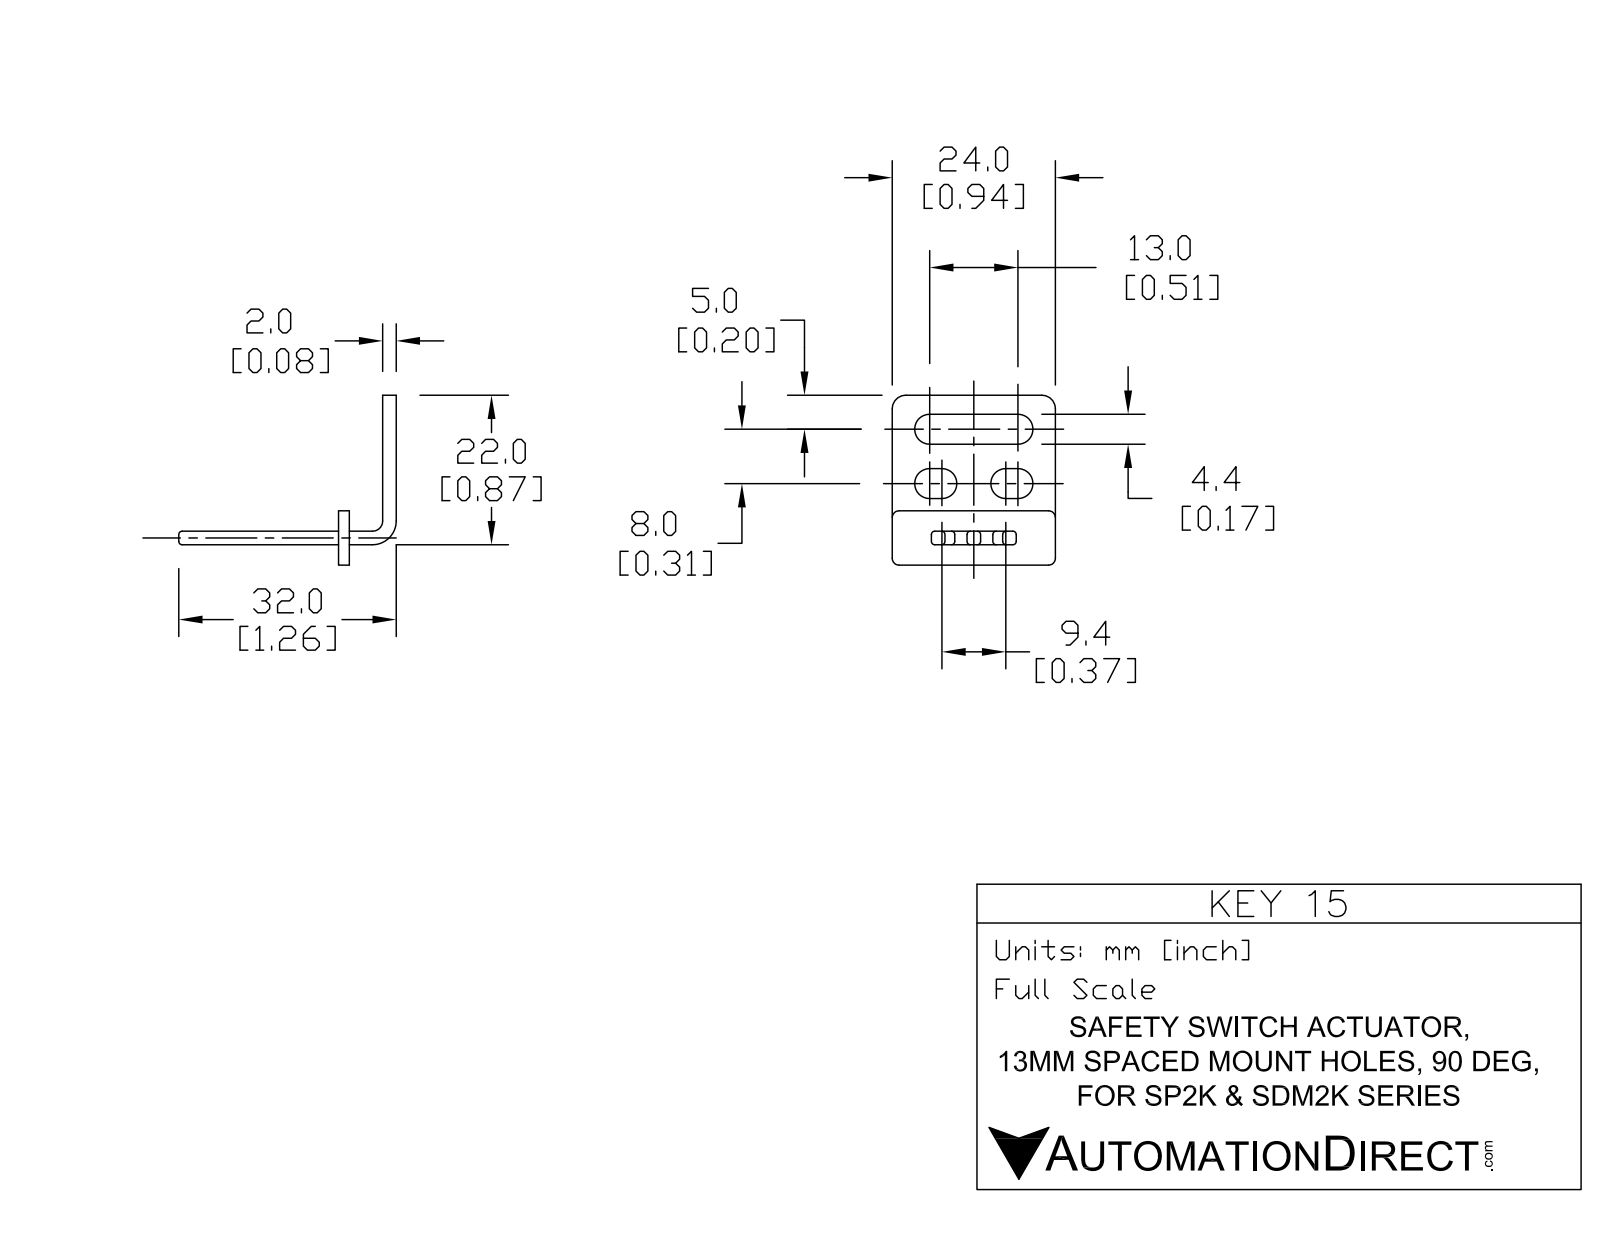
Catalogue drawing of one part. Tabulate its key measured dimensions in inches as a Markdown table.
| quantity | value |
| --- | --- |
| part name | KEY15 |
| STEP written by | SolidWorks 2019 (CONFIG_CONTROL_DESIGN) |
| units | inches |
| bodies | 2 solids, 169 faces (60 planar, 81 cylindrical, 28 other) |
| overall size | 1.26 × 0.984 × 0.945 |
| volume | 0.103 in³ |
| surface area | 3.815 in² |
| partial cylindrical surfaces (radius × count) | 0.02 × 42, 0.039 × 8, 0.087 × 6, 0.008 × 4, 0.059 × 4, 0.031 × 1, 0.11 × 1 |
| main face-to-face distances | 0.079, 0.335, 0.256, 0.398, 0.319, 0.063, 0.118, 0.197, 0.945, 0.207 |
